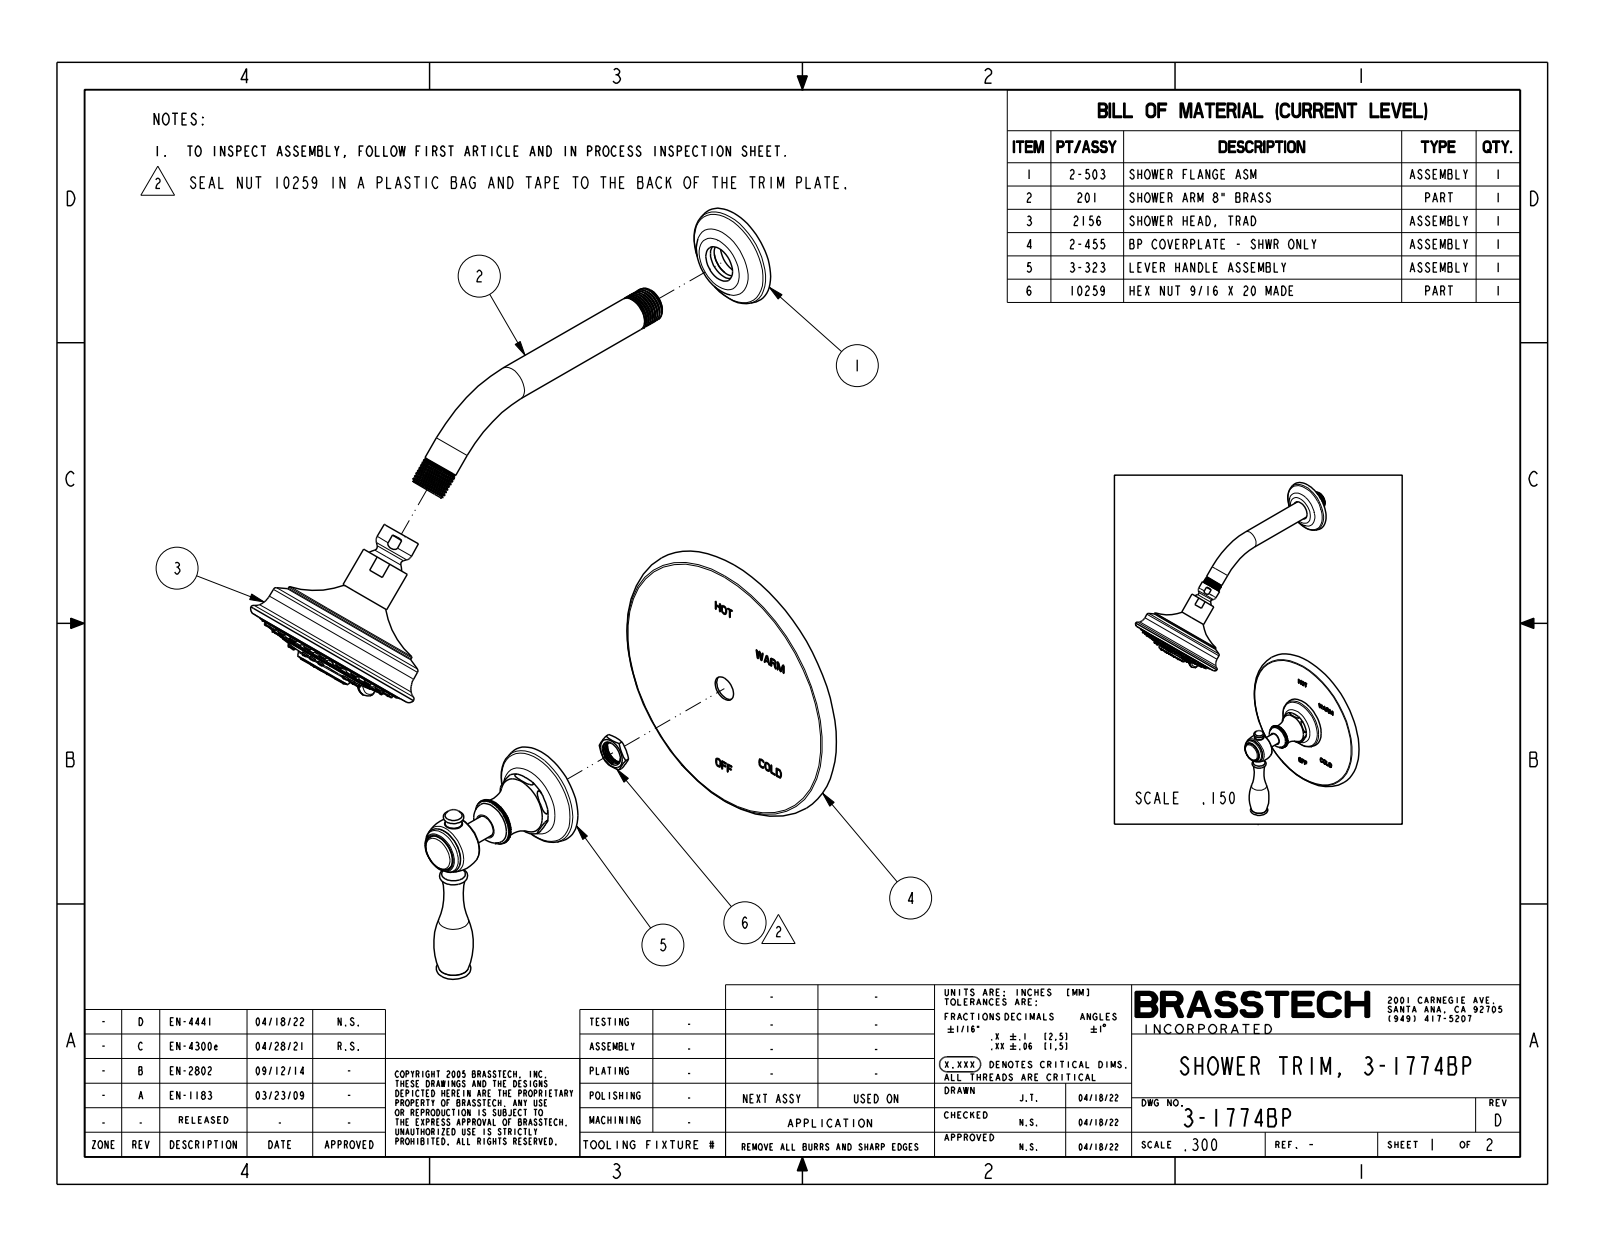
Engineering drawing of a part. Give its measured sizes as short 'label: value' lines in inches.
name: 3-1774BP
written by: CREO PARAMETRIC BY PTC INC, 2018400 (CONFIG_CONTROL_DESIGN)
unit: in
bodies: 2 solids, 1608 faces (613 planar, 204 cylindrical, 791 other)
size: 16.831 × 10.05 × 6.625
volume: 35.93 in³; area: 171.1 in²
holes: 8× ⌀0.059, 1× ⌀0.41, 1× ⌀0.855, 1× ⌀0.925
bosses: 39× ⌀0.142, 23× ⌀0.165, 2× ⌀0.813, 1× ⌀3.81, 1× ⌀3.724, 1× ⌀3.24, 1× ⌀2.323, 1× ⌀1.15
rounds: 8× R0.079, 2× R0.02, 1× R0.138, 1× R0.472, 1× R0.512, 1× R0.63
face distances: 0.313, 0.48, 0.167, 0.063, 0.118, 0.181, 2.853, 2.54, 2.373, 2.881
hole spacings: 0.579, 0.443, 1.069, 0.818, 0.819, 1.157, 0.443, 1.069
